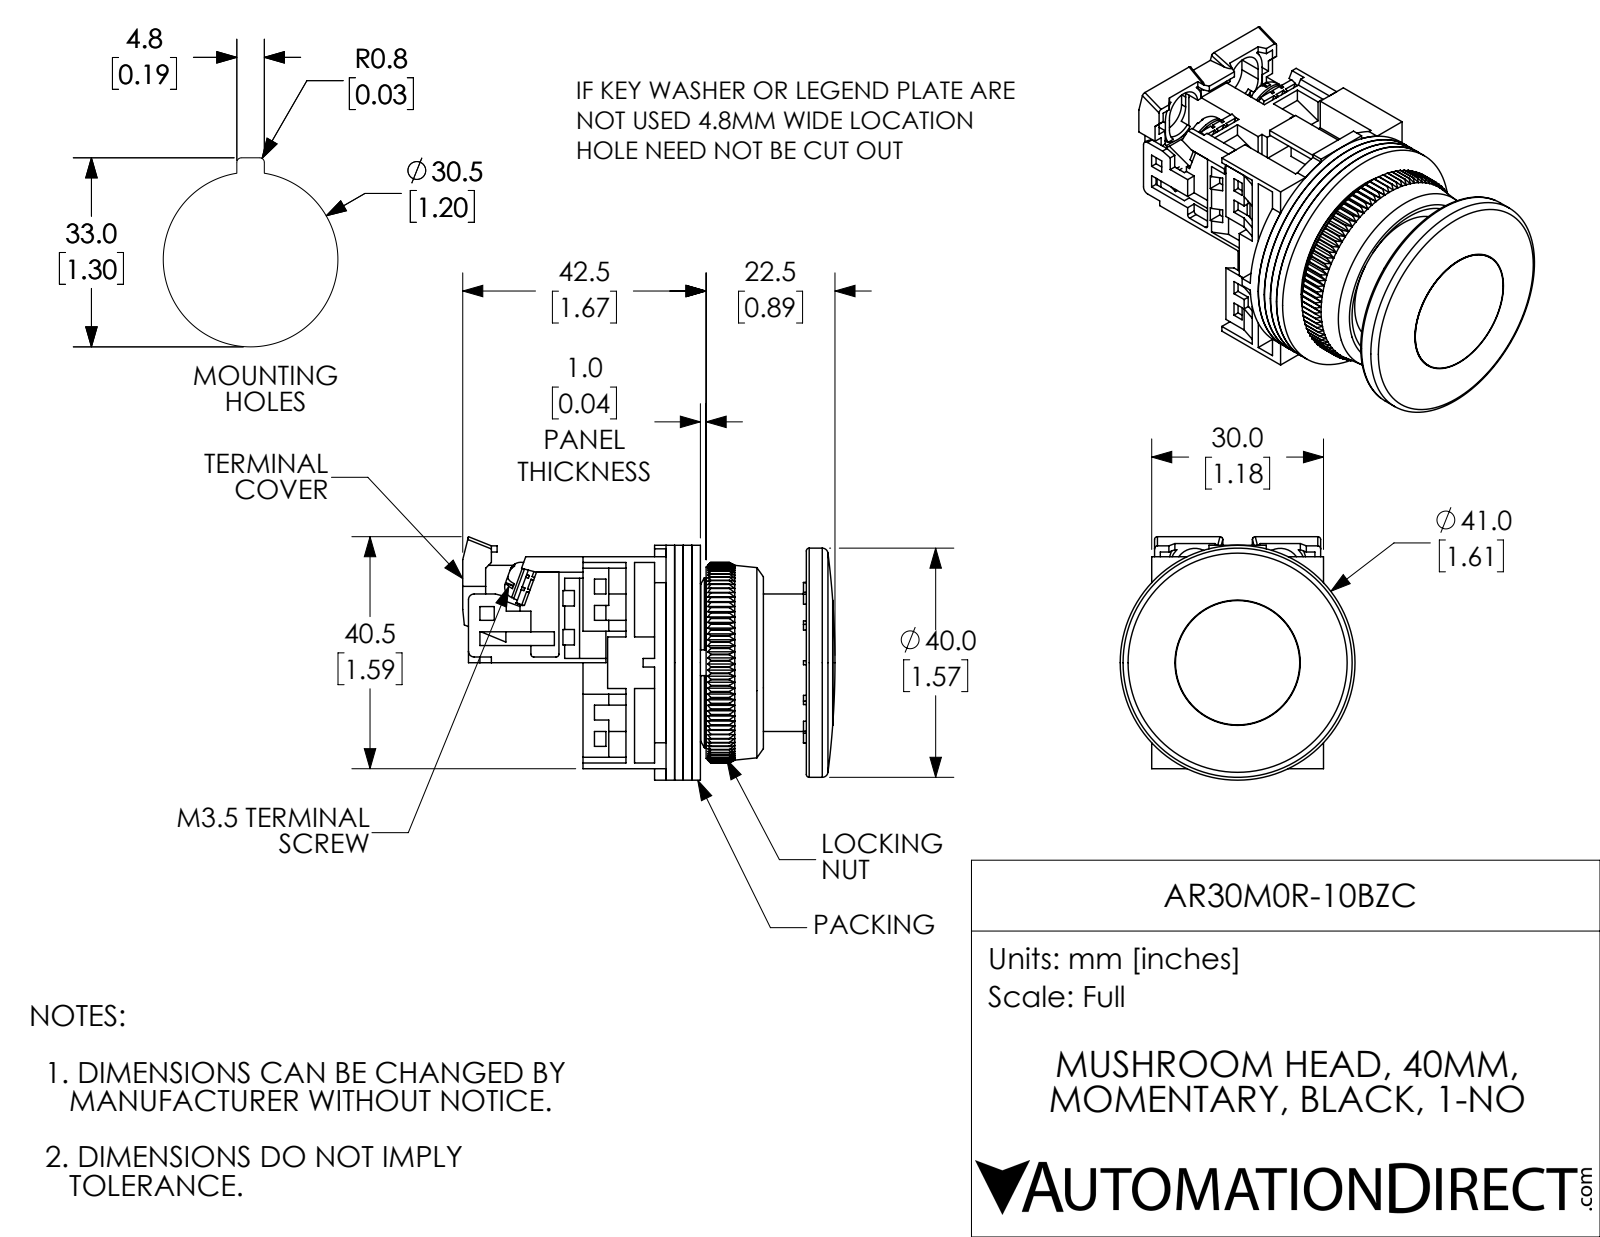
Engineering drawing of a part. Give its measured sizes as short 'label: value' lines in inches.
name: AR30M0R-10BZC
written by: SolidWorks 2017 (AUTOMOTIVE_DESIGN)
unit: in
bodies: 15 solids, 1278 faces (819 planar, 260 cylindrical, 199 other)
size: 2.559 × 1.673 × 1.614
volume: 2.225 in³; area: 48.33 in²
holes: 4× ⌀0.138, 2× ⌀0.142, 1× ⌀0.118, 1× ⌀0.709, 1× ⌀0.945, 1× ⌀1.122, 1× ⌀1.252, 1× ⌀1.417
bosses: 2× ⌀0.26, 2× ⌀0.138, 1× ⌀1.614, 1× ⌀1.575, 1× ⌀1.181, 1× ⌀0.854
rounds: 8× R0.059, 6× R0.02, 2× R0.039, 2× R0.138, 2× R0.177, 1× R0.118, 1× R0.398, 1× R0.449
face distances: 0.059, 0.118, 0.177, 0.039, 0.079, 0.689, 0.728, 0.866, 0.807, 1.417
hole spacings: 0.579, 0.61
